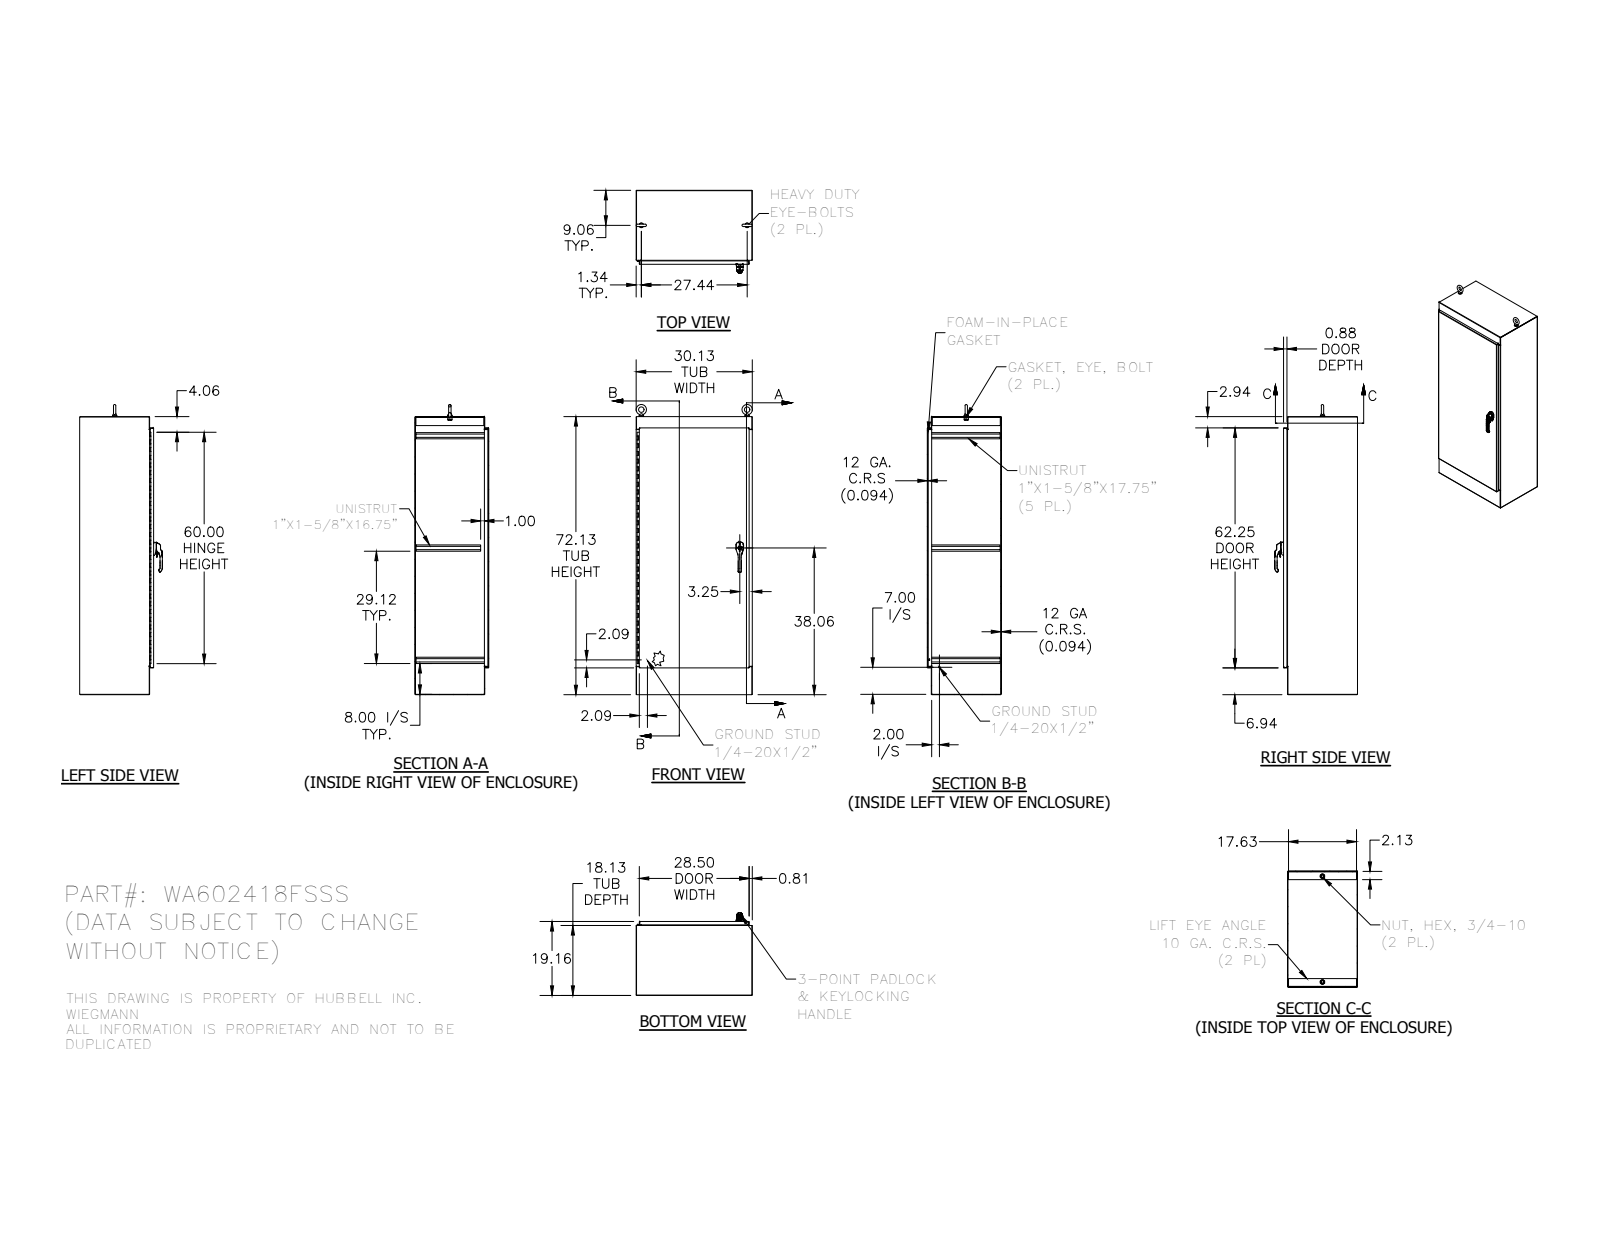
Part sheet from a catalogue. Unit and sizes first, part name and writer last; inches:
Units: inches
Overall size (bounding box): 75.248 × 30.125 × 21.409
Round holes (diameter × count): ⌀0.276 ×8, ⌀0.2 ×4, ⌀0.213 ×3, ⌀0.28 ×3, ⌀0.315 ×2, ⌀0.402 ×2, ⌀0.407 ×2, ⌀0.413 ×2, ⌀0.642 ×2, ⌀0.813 ×2, ⌀0.122 ×1, ⌀0.124 ×1
Round bosses / shafts (diameter × count): ⌀0.25 ×3, ⌀1.25 ×2, ⌀1.12 ×2, ⌀0.75 ×2, ⌀0.531 ×2, ⌀0.526 ×2, ⌀0.435 ×2, ⌀0.337 ×2
Partial cylindrical surfaces — rounded edges, fillets, slot ends (radius × count): R0.02 ×170, R0.012 ×101, R0.019 ×21, R0.01 ×16, R0.031 ×16, R0.053 ×14, R0.079 ×14, R0.125 ×14
Main face-to-face distances: 0.094, 19.067, 30.031, 18.973, 19.161, 29.938, 30.125, 72.031, 18.031, 1.035
Hole centre spacings: 0.38, 0.382, 0.382, 0.762, 0.764, 0.886, 1.144, 1.271
Volume: 877.5 in³ · Surface area: 18 580 in²
Bodies: 46 solids, 2879 faces (1224 planar, 1007 cylindrical, 648 other)
Part name (STEP PRODUCT): WA723018FSBLR; WA3018FSTOP; WA3018FSBTM; WA7230FSDR (+8 more)
STEP written by: Autodesk Inventor 2014 (AUTOMOTIVE_DESIGN)
